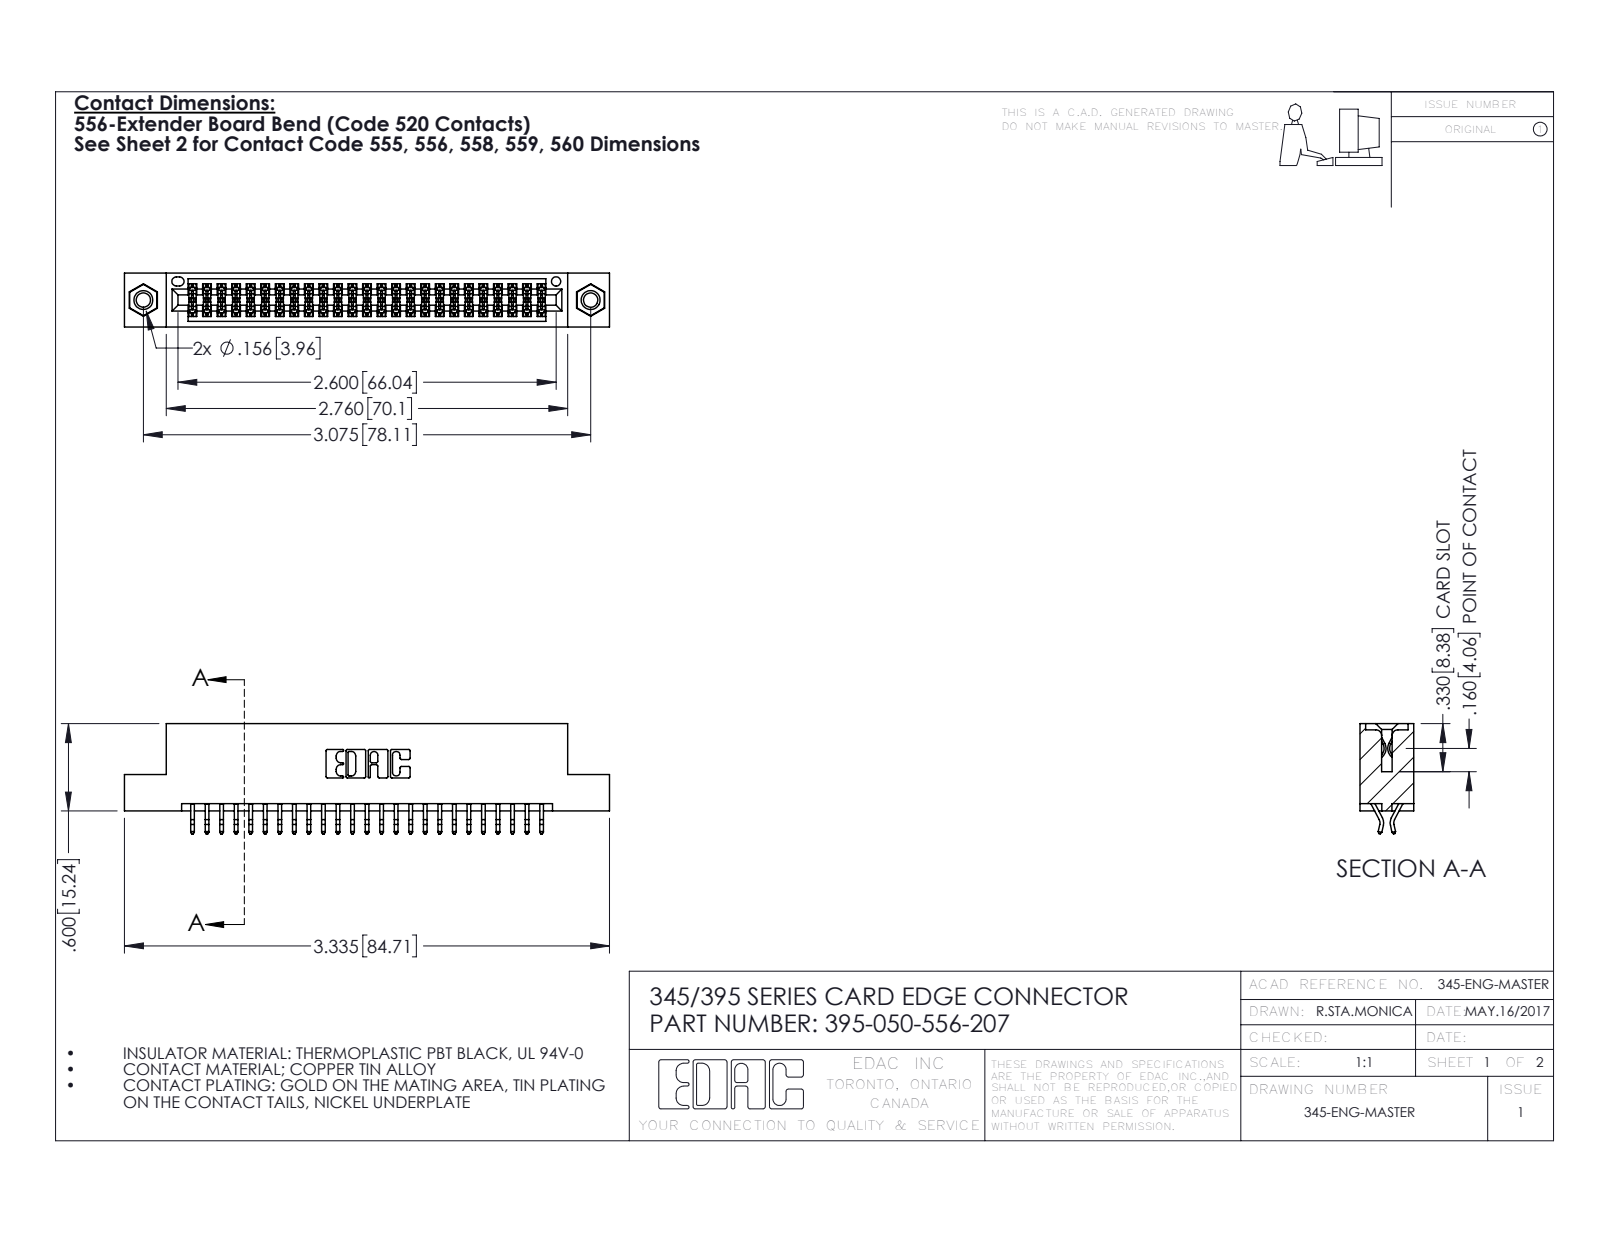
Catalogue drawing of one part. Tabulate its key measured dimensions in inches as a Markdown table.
| quantity | value |
| --- | --- |
| part name | 345-292-001_556 Tail; 345-250-001_345-250-005-103; 395-050-556-207; 345 Part_Flush Mounting Lugs - 0.156 Dia-TI |
| STEP written by | SolidWorks 2016 (CONFIG_CONTROL_DESIGN) |
| units | inches |
| bodies | 53 solids, 2986 faces (1962 planar, 1008 cylindrical, 16 other) |
| overall size | 3.335 × 0.757 × 0.37 |
| volume | 0.492 in³ |
| surface area | 17.92 in² |
| round holes (diameter × count) | 0.098 × 2, 0.125 × 2, 0.156 × 2, 0.064 × 1 |
| round bosses / shafts (diameter × count) | 0.155 × 2 |
| partial cylindrical surfaces (radius × count) | 0.006 × 75, 0.01 × 22, 0.007 × 6, 0.031 × 6, 0.026 × 3, 0.01 × 2, 0.014 × 2, 0.019 × 2 |
| main face-to-face distances | 0.072, 0.298, 0.2, 0.37, 0.025, 0.098, 0.272, 0.225, 0.175, 0.149 |
| hole center spacings | 0.27, 2.84, 3.075 |
